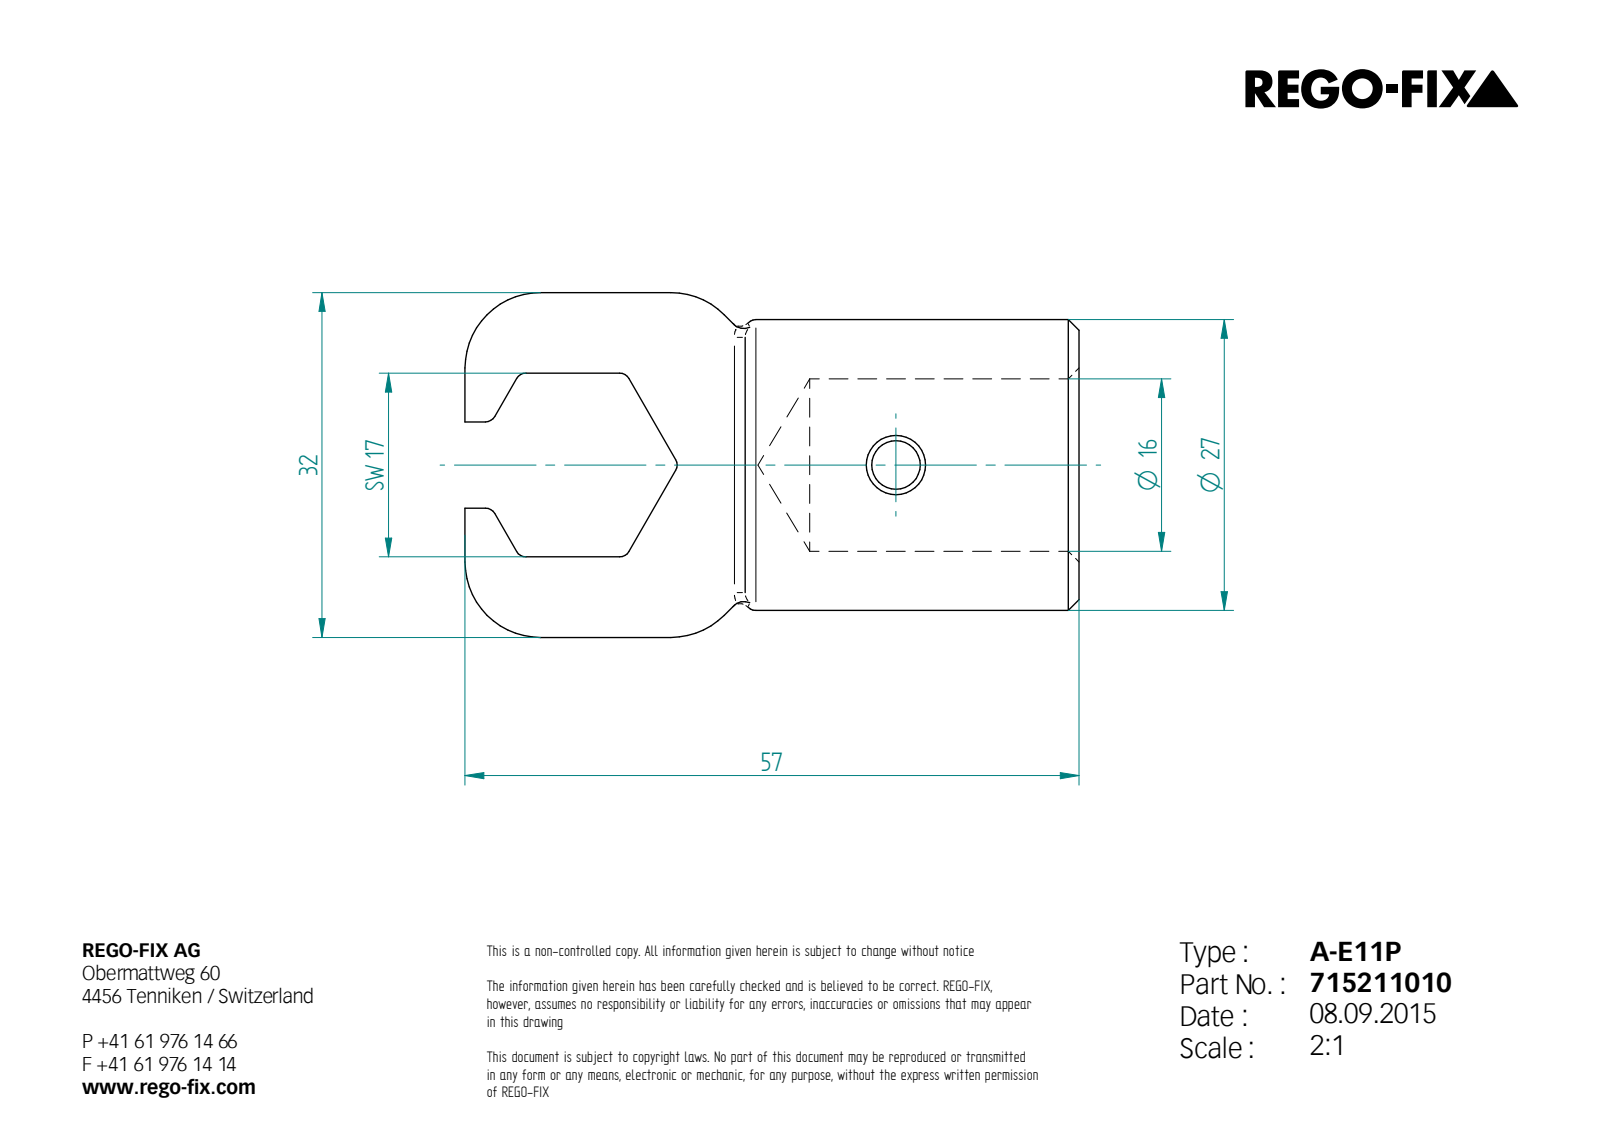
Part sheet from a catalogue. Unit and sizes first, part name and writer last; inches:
Units: inches
Overall size (bounding box): 2.244 × 1.26 × 1.063
Round holes (diameter × count): ⌀0.177 ×1, ⌀0.217 ×1, ⌀0.63 ×1
Round bosses / shafts (diameter × count): ⌀1.063 ×1
Partial cylindrical surfaces — rounded edges, fillets, slot ends (radius × count): R0.039 ×9, R0.276 ×4
Main face-to-face distances: 0.236, 1.22, 0.294, 0.966, 1.26, 1.024, 2.244, 0.672, 0.671, 0.472
Volume: 0.931 in³ · Surface area: 10.38 in²
Bodies: 1 solid, 48 faces (19 planar, 18 cylindrical, 11 other)
STEP written by: Unknown (AUTOMOTIVE_DESIGN)
